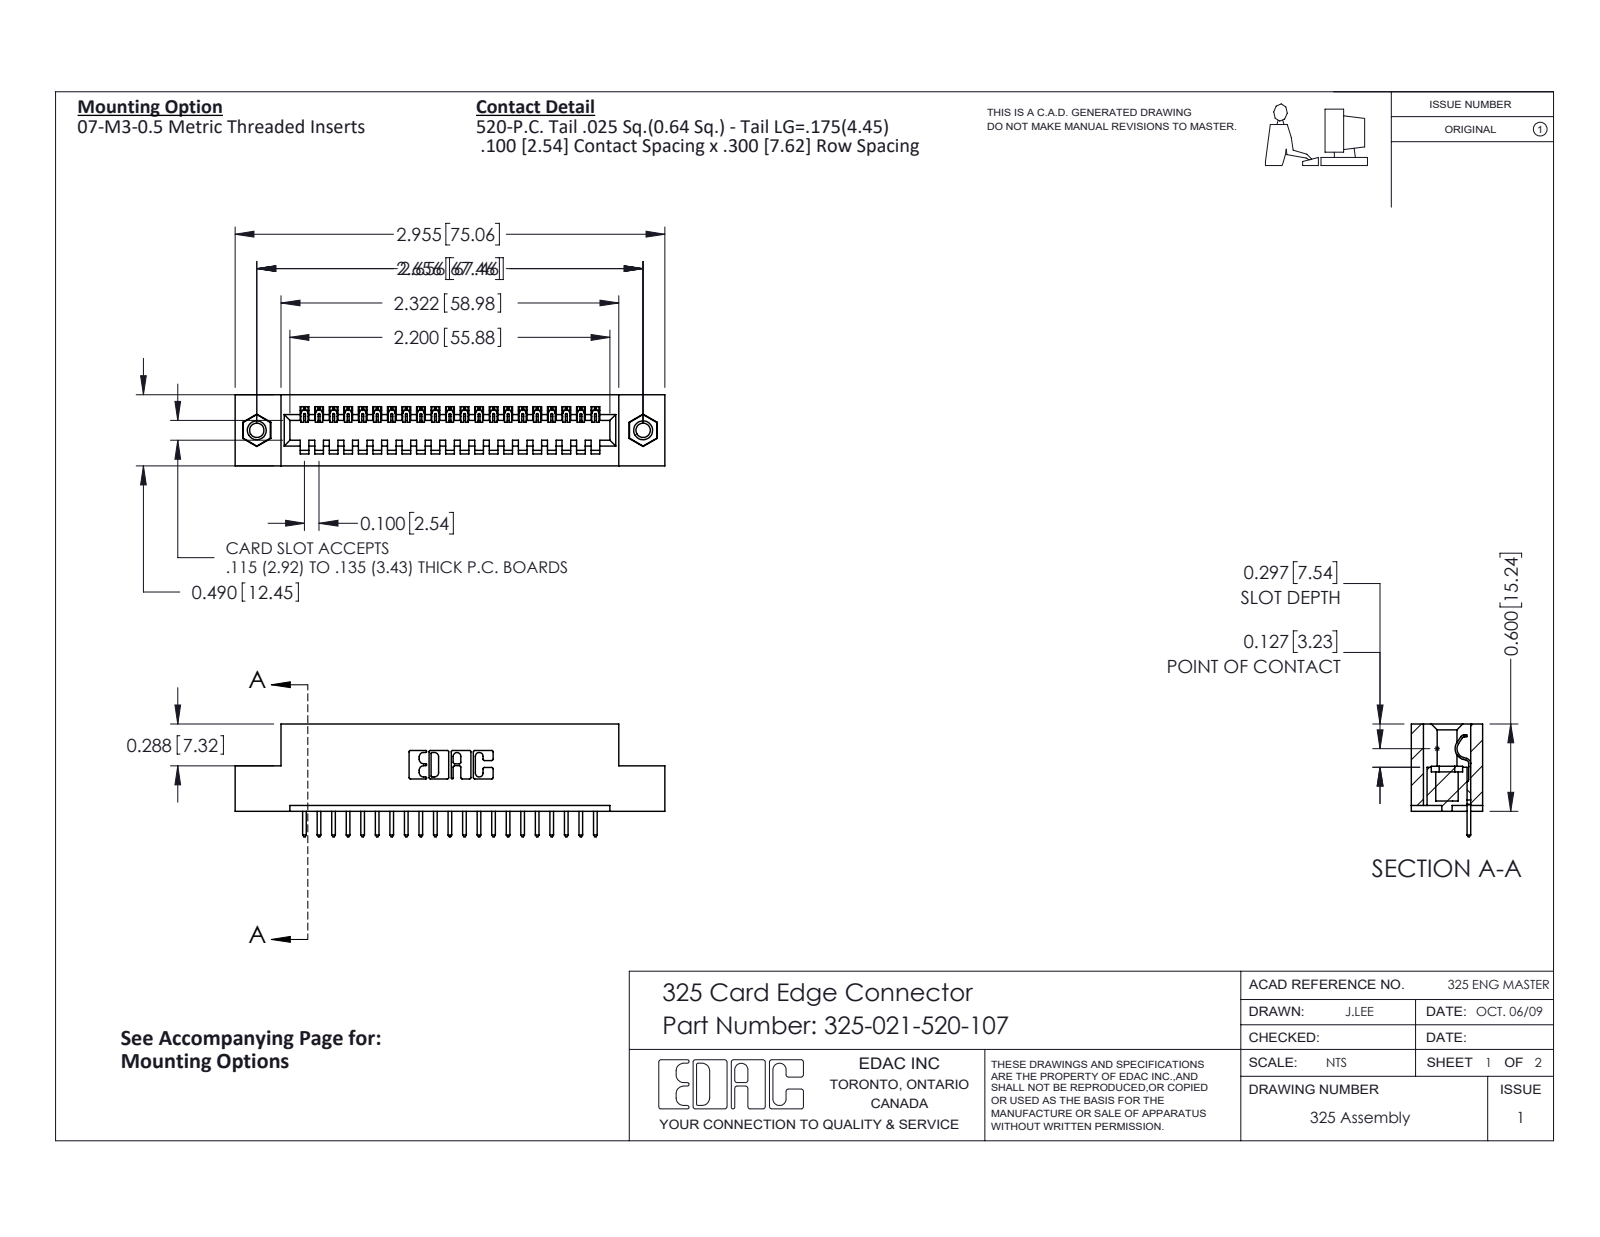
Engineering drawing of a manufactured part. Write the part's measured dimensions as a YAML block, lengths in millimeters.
part_name: "325-021-520-107; 345-250-001_345-250-005-103; 325 Part_TI; 325-292-001_325-293-120"
step_written_by: "SolidWorks 2016 (CONFIG_CONTROL_DESIGN)"
units: millimeters
bodies: {solids: 24, faces: 1392, planar: 984, cylindrical: 392, other: 16}
overall_size: [75.1, 19.7, 12.4]
volume: 9290
surface_area: 9606
round_holes:
  - {diameter: 2.5, count: 2}
  - {diameter: 3.2, count: 2}
  - {diameter: 4.1, count: 2}
round_bosses_or_shafts:
  - {diameter: 3.9, count: 2}
partial_cylinders:
  - {radius: 0.2, count: 42}
  - {radius: 0.3, count: 42}
  - {radius: 0.3, count: 22}
  - {radius: 0.2, count: 6}
  - {radius: 0.8, count: 6}
  - {radius: 0.7, count: 3}
  - {radius: 0.4, count: 1}
  - {radius: 0.6, count: 1}
face_to_face_distances: [2.1, 10.3, 12.4, 7.6, 2.7, 9.7, 0.6, 15.2, 1, 2.5]
hole_center_spacings: [67.5]
